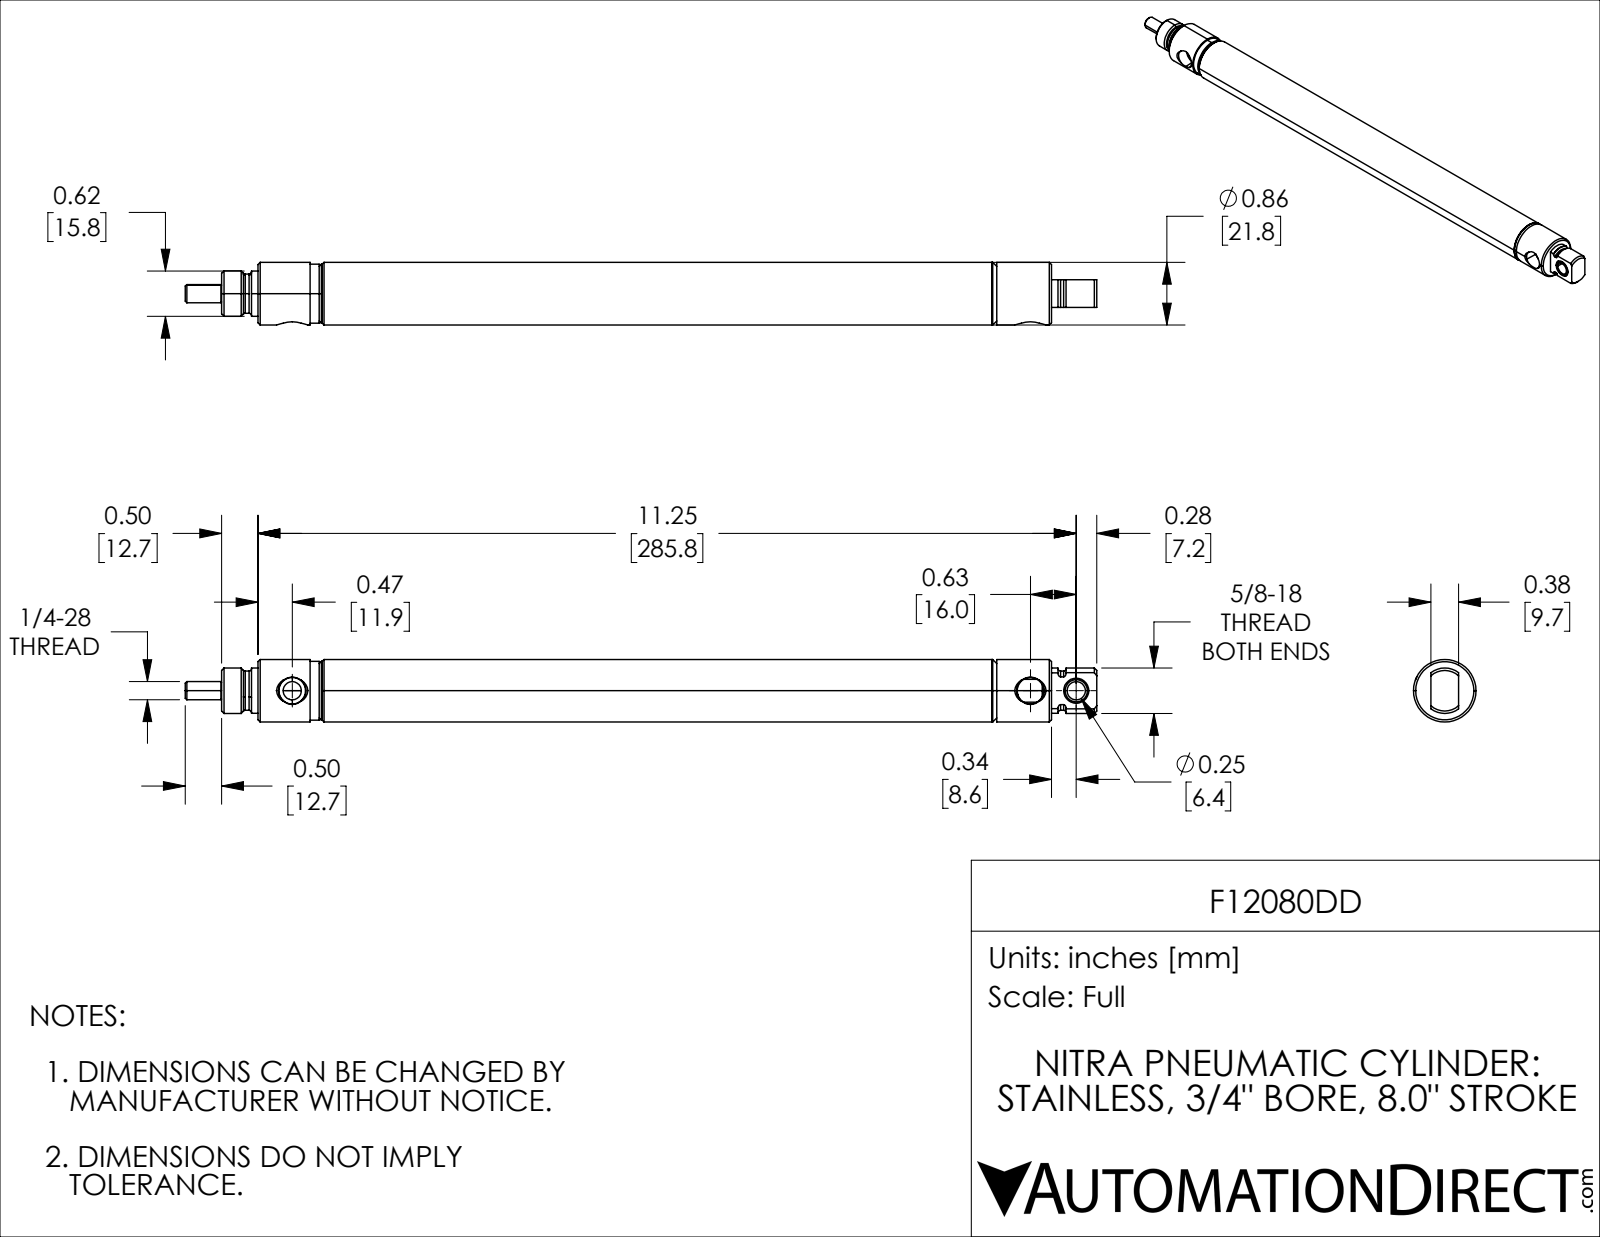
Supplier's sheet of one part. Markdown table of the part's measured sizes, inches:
| quantity | value |
| --- | --- |
| part name | F12080DD_7; F12080DD; F12080DD_9; F12080DD_3 (+2 more) |
| STEP written by | SolidWorks 2021 (CONFIG_CONTROL_DESIGN) |
| units | inches |
| bodies | 5 solids, 158 faces (29 planar, 61 cylindrical, 68 other) |
| overall size | 12.532 × 0.86 × 0.86 |
| volume | 3.179 in³ |
| surface area | 72.52 in² |
| round holes (diameter × count) | 0.25 × 1, 0.251 × 1, 0.274 × 1, 0.312 × 1, 0.346 × 1, 0.363 × 1, 0.5 × 1, 0.702 × 1 |
| round bosses / shafts (diameter × count) | 0.86 × 1, 0.81 × 1, 0.762 × 1, 0.625 × 1, 0.622 × 1, 0.539 × 1, 0.25 × 1, 0.23 × 1 |
| partial cylindrical surfaces (radius × count) | 0.269 × 1 |
| main face-to-face distances | 0.844, 1.594, 10.438, 8, 8.844, 9.816, 1.816, 0.972, 0.5, 0.38 |
| hole center spacings | 0.63, 10.15, 10.78 |
